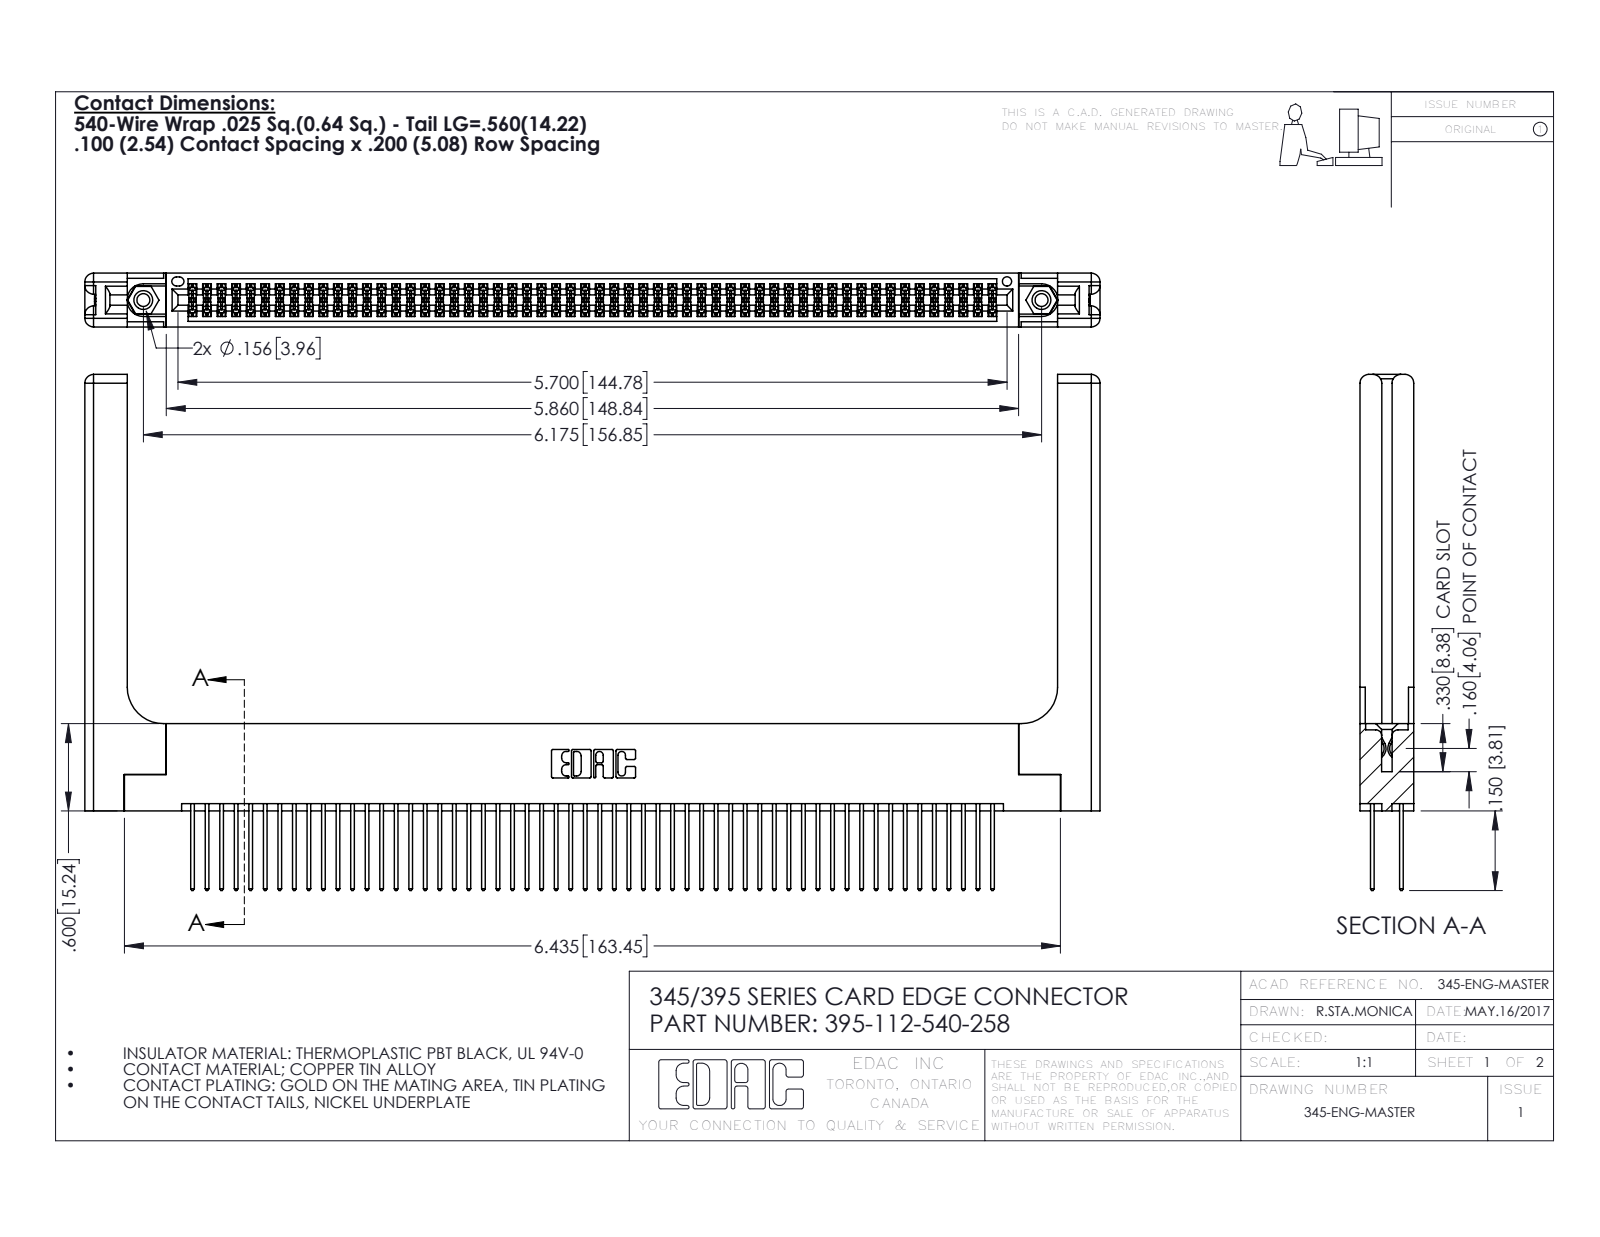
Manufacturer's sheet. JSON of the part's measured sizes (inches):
{"part_name": "345 Part_Flush Mounting Lugs - 0.156 Dia-TH; 345-250-001_345-250-001-102; 395-112-540-258; 345-220-058_345-220-058 (+1 more)", "step_written_by": "SolidWorks 2016 (CONFIG_CONTROL_DESIGN)", "units": "inches", "bodies": {"solids": 117, "faces": 5982, "planar": 3924, "cylindrical": 1998, "other": 60}, "overall_size": [6.979, 3.547, 0.37], "volume_in3": 1.602, "surface_area_in2": 52.04, "round_holes": [[0.089, 2], [0.125, 2], [0.156, 2], [0.064, 1]], "round_bosses_or_shafts": [[0.155, 2]], "partial_cylinders_radius": [[0.006, 168], [0.01, 112], [0.01, 22], [0.06, 16], [0.007, 6], [0.031, 6], [0.026, 3], [0.014, 2]], "face_to_face_distances": [0.072, 0.298, 0.37, 0.2, 0.098, 0.272, 0.025, 0.225, 0.175, 0.148], "hole_center_spacings": [0.27, 5.939, 6.175]}
